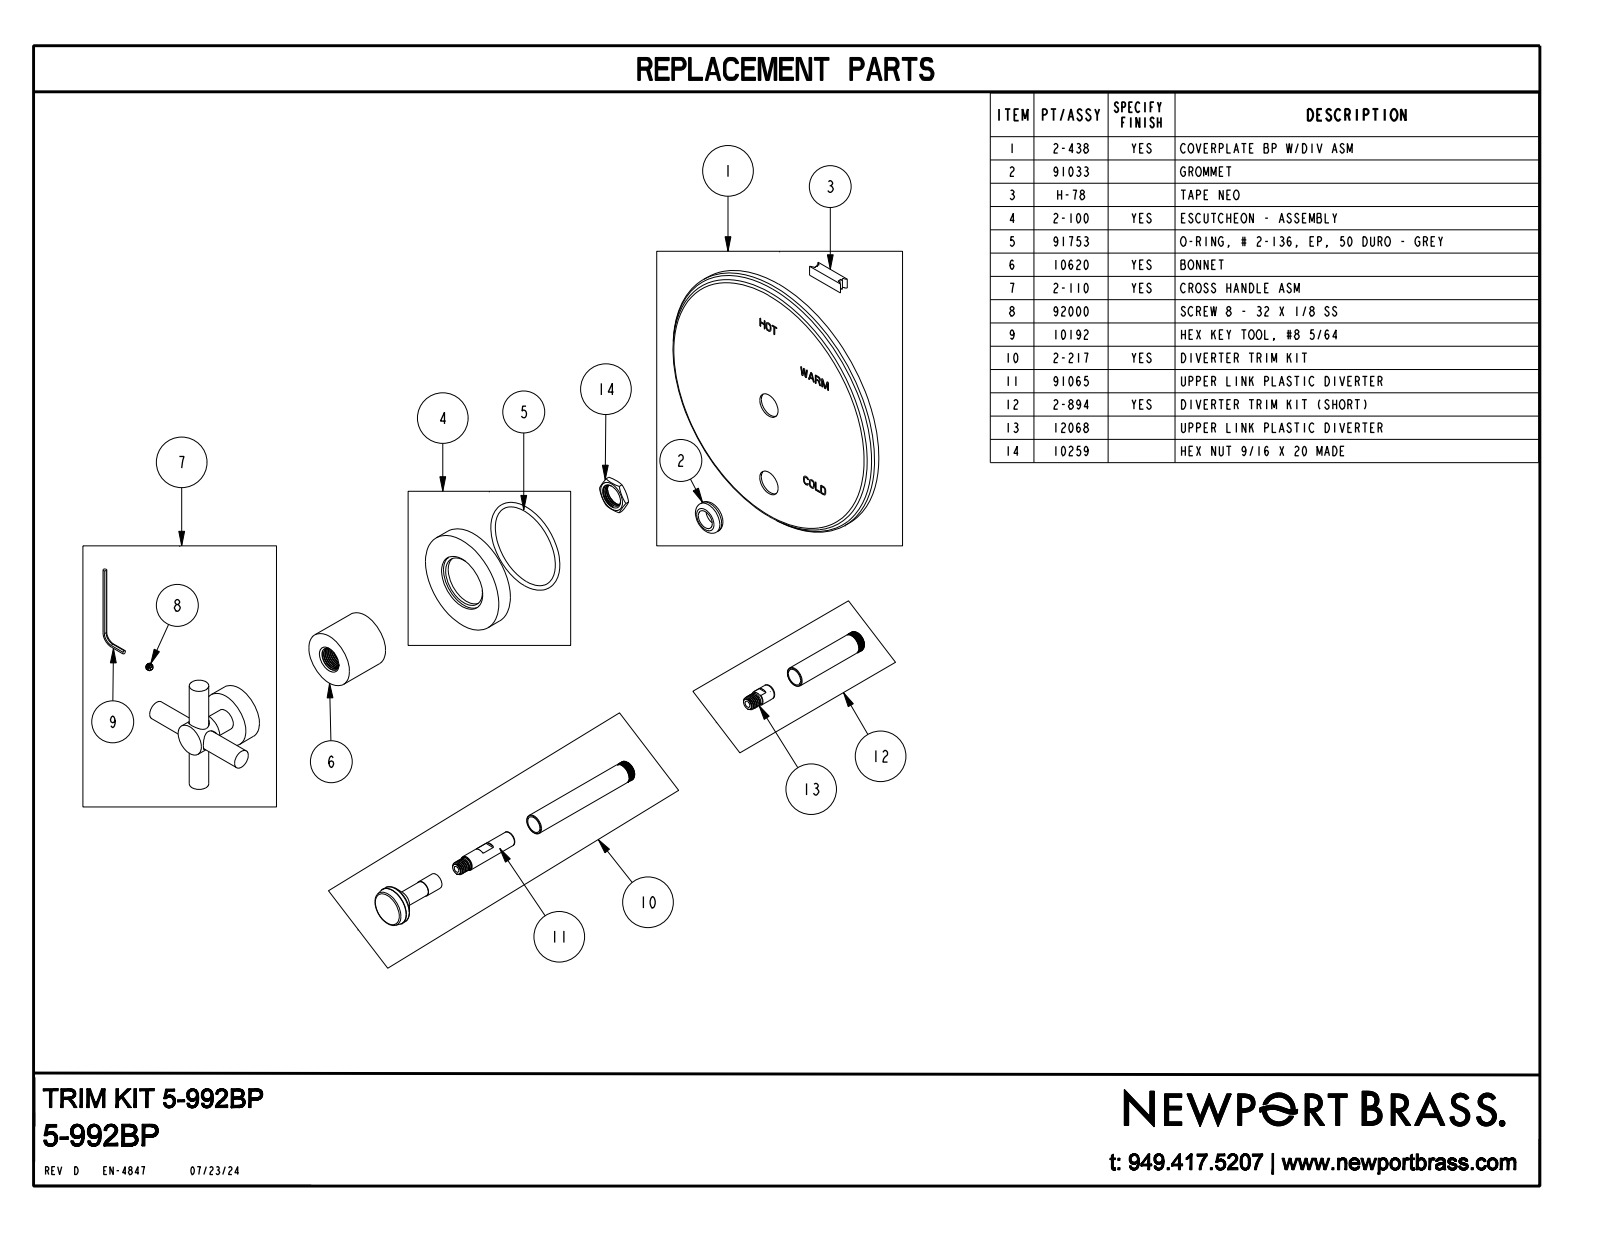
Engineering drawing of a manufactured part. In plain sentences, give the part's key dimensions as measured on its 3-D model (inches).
The part is named "5-992BP". Its 3-D file was written by "CREO PARAMETRIC BY PTC INC, 2018400 (CONFIG_CONTROL_DESIGN)". It is 1 solid with 335 faces: 279 planar, 36 cylindrical and 20 other. Overall it measures 6.5 by 6.5 by 3.416 inches. Its volume is 15.26 cubic inches and its surface area 94.72 square inches. Round holes: 2 of diameter 0.47. Round bosses or shafts: 2 of diameter 0.445, 1 of diameter 6.5, 1 of diameter 2.375, 1 of diameter 1.313, 1 of diameter 0.9, 1 of diameter 0.75, 1 of diameter 0.5, 1 of diameter 0.472. The main face-to-face distances are 0.313, 0.688, 0.375, 1.796, 1.816, 1.483, 1.503, 1.108, 1.128, 0.02.
